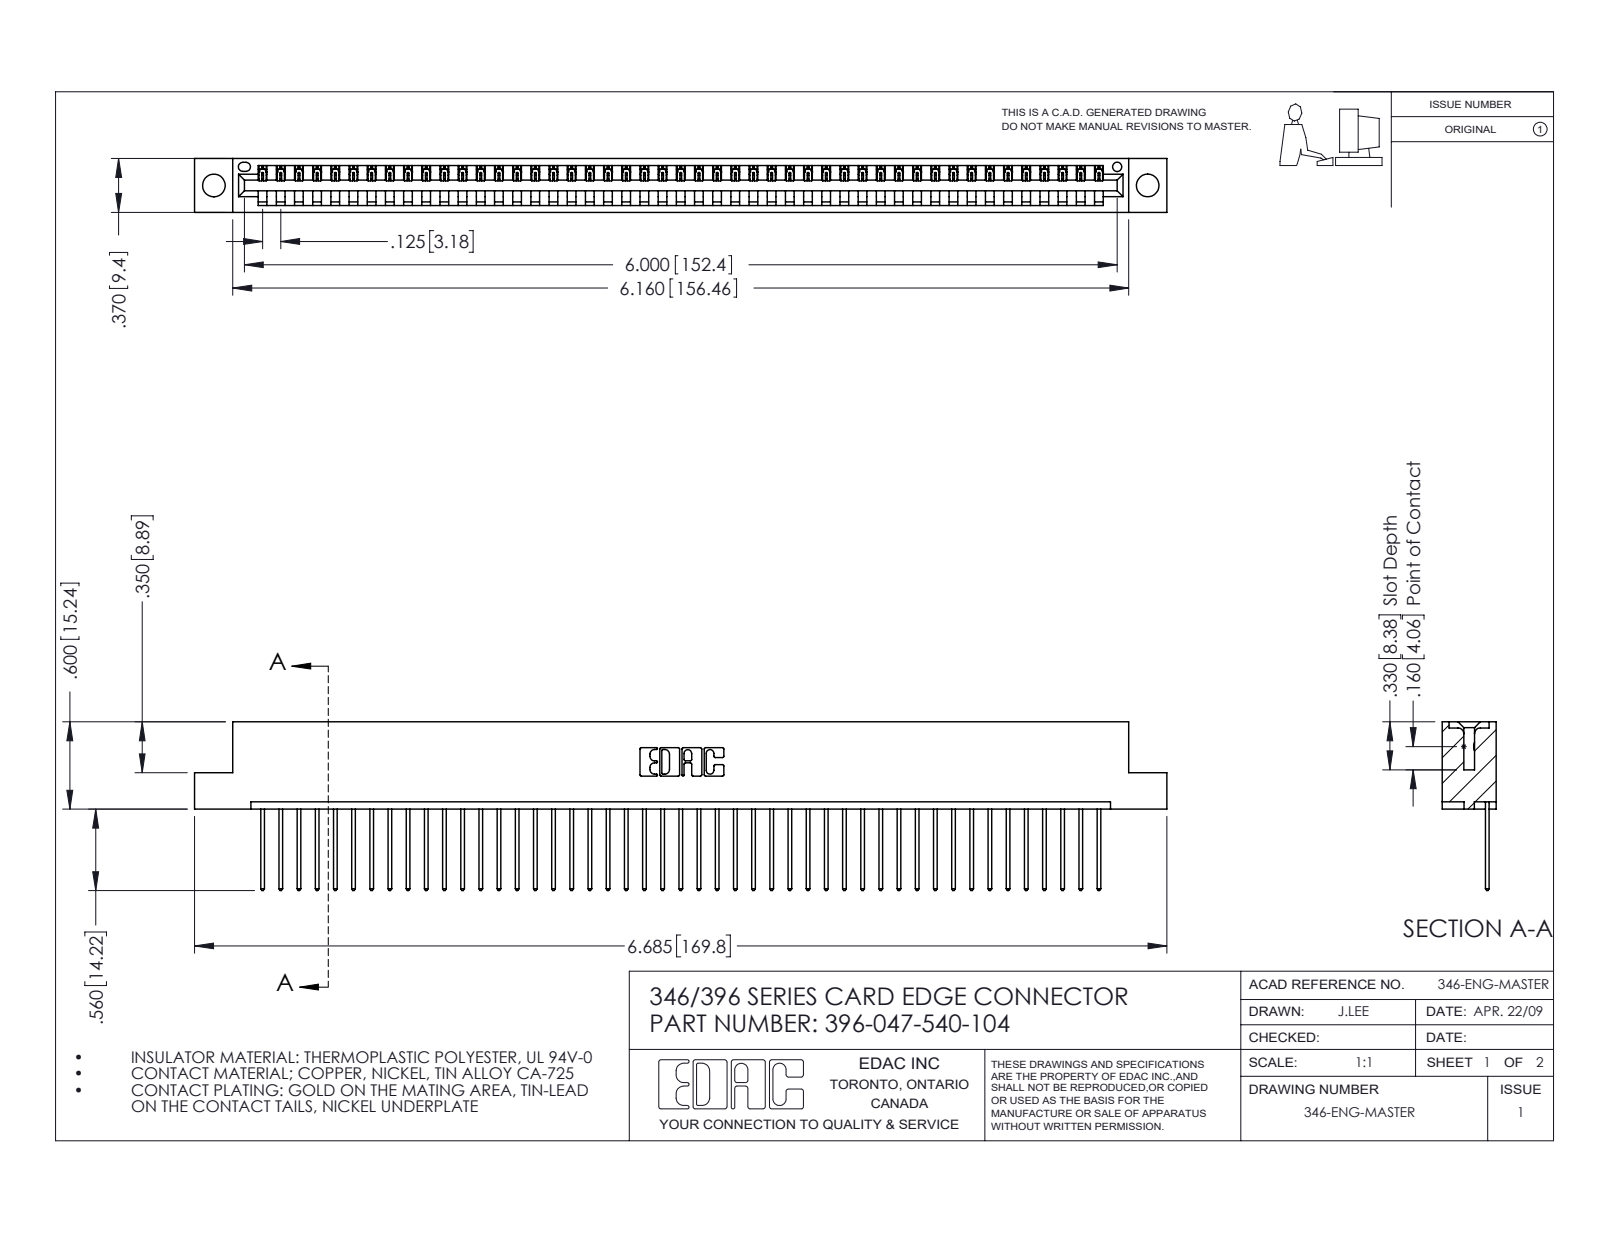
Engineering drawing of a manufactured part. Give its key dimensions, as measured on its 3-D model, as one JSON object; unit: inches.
{"part_name": "396-047-540-104; 345-292-001_345-293-140; 346 Part_Flush Mounting Lugs - 0.156 Dia-TH", "step_written_by": "SolidWorks 2016 (CONFIG_CONTROL_DESIGN)", "units": "inches", "bodies": {"solids": 48, "faces": 2848, "planar": 1956, "cylindrical": 892, "other": 0}, "overall_size": [6.685, 1.16, 0.37], "volume_in3": 0.992, "surface_area_in2": 32.01, "round_holes": [[0.156, 2], [0.064, 1]], "partial_cylinders_radius": [[0.006, 94], [0.01, 94], [0.01, 22], [0.007, 6], [0.031, 6], [0.026, 3], [0.031, 2], [0.04, 2]], "face_to_face_distances": [0.048, 0.322, 0.37, 0.25, 0.072, 0.298, 0.025, 0.148, 0.222, 0.1], "hole_center_spacings": [0.246, 6.211, 6.42]}
